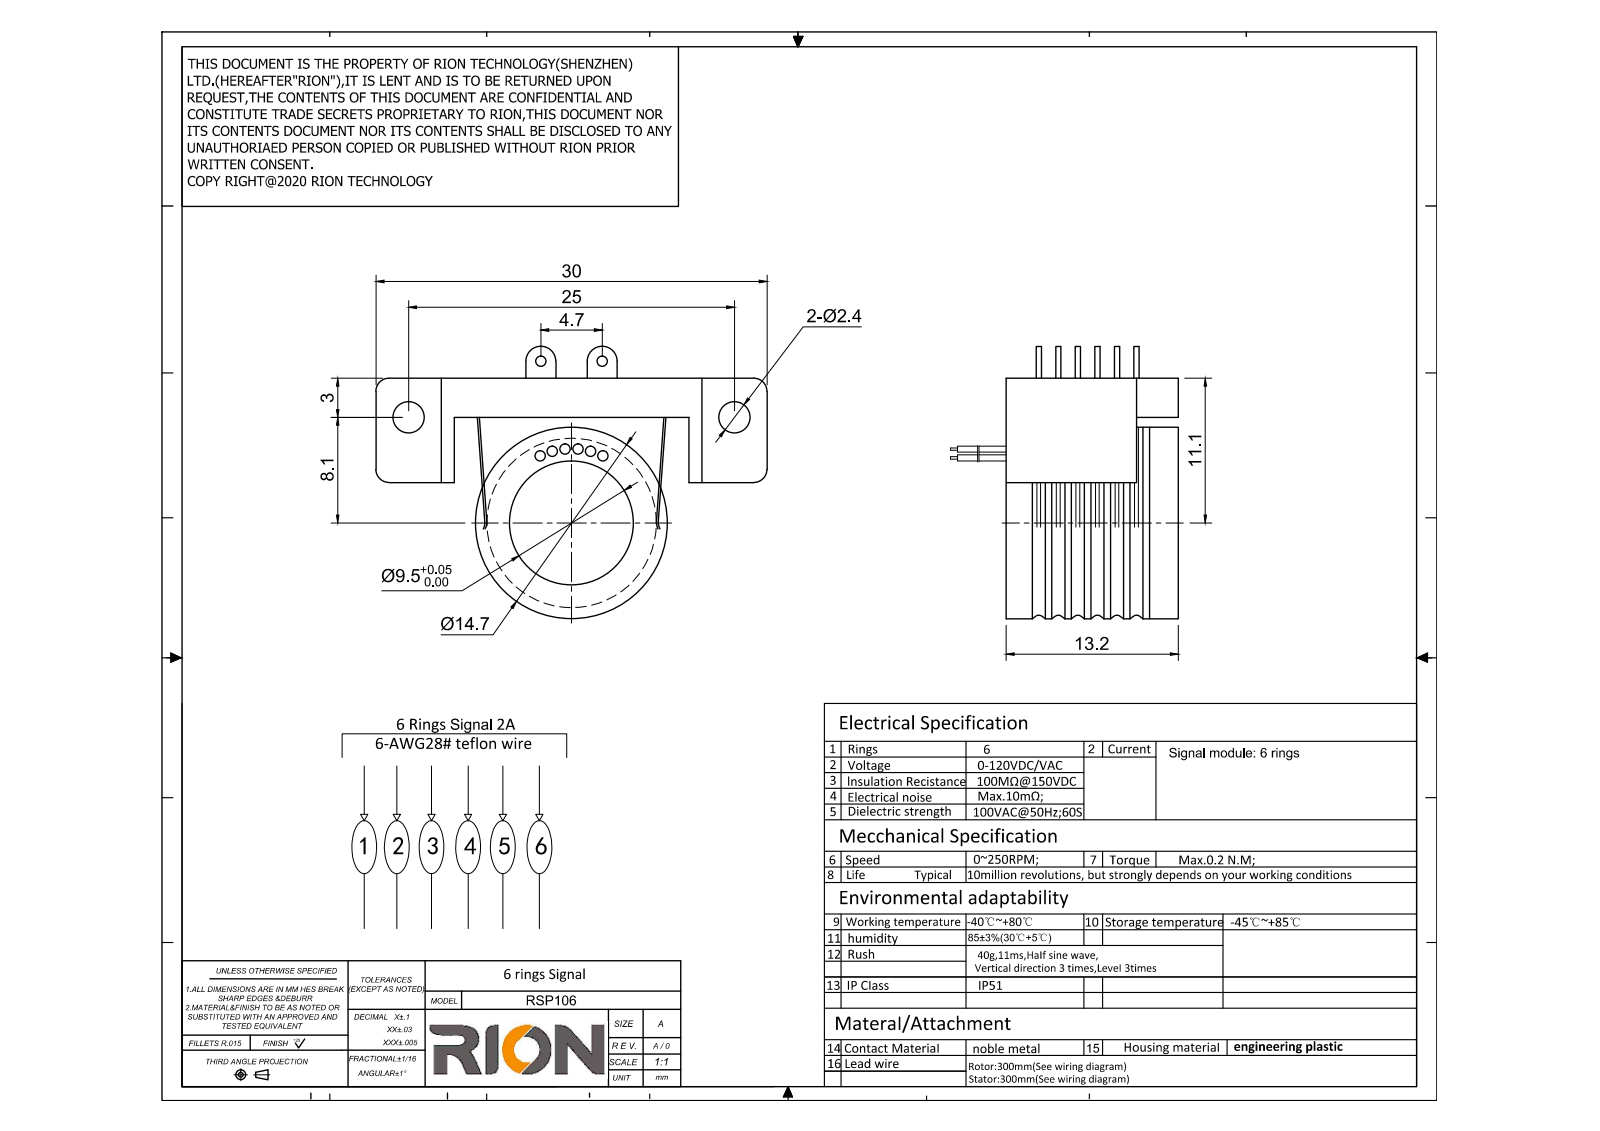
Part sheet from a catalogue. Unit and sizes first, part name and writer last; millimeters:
Units: millimetres
Overall size (bounding box): 30 × 20.9 × 13.2
Round holes (diameter × count): ⌀0.8 ×2, ⌀2.4 ×2, ⌀9.5 ×1
Round bosses / shafts (diameter × count): ⌀14.7 ×1
Partial cylindrical surfaces — rounded edges, fillets, slot ends (radius × count): R1 ×4, R1.15 ×2
Main face-to-face distances: 3, 13.2, 5, 6, 24, 8, 3.2, 10, 18, 30
Hole centre spacings: 11.02, 12.62, 14.89, 15.46, 4.7, 25
Volume: 2 899 mm³ · Surface area: 2 881 mm²
Bodies: 1 solid, 178 faces (52 planar, 42 cylindrical, 84 other)
Part name (STEP PRODUCT): RSP106
STEP written by: SolidWorks 2014 (CONFIG_CONTROL_DESIGN)
